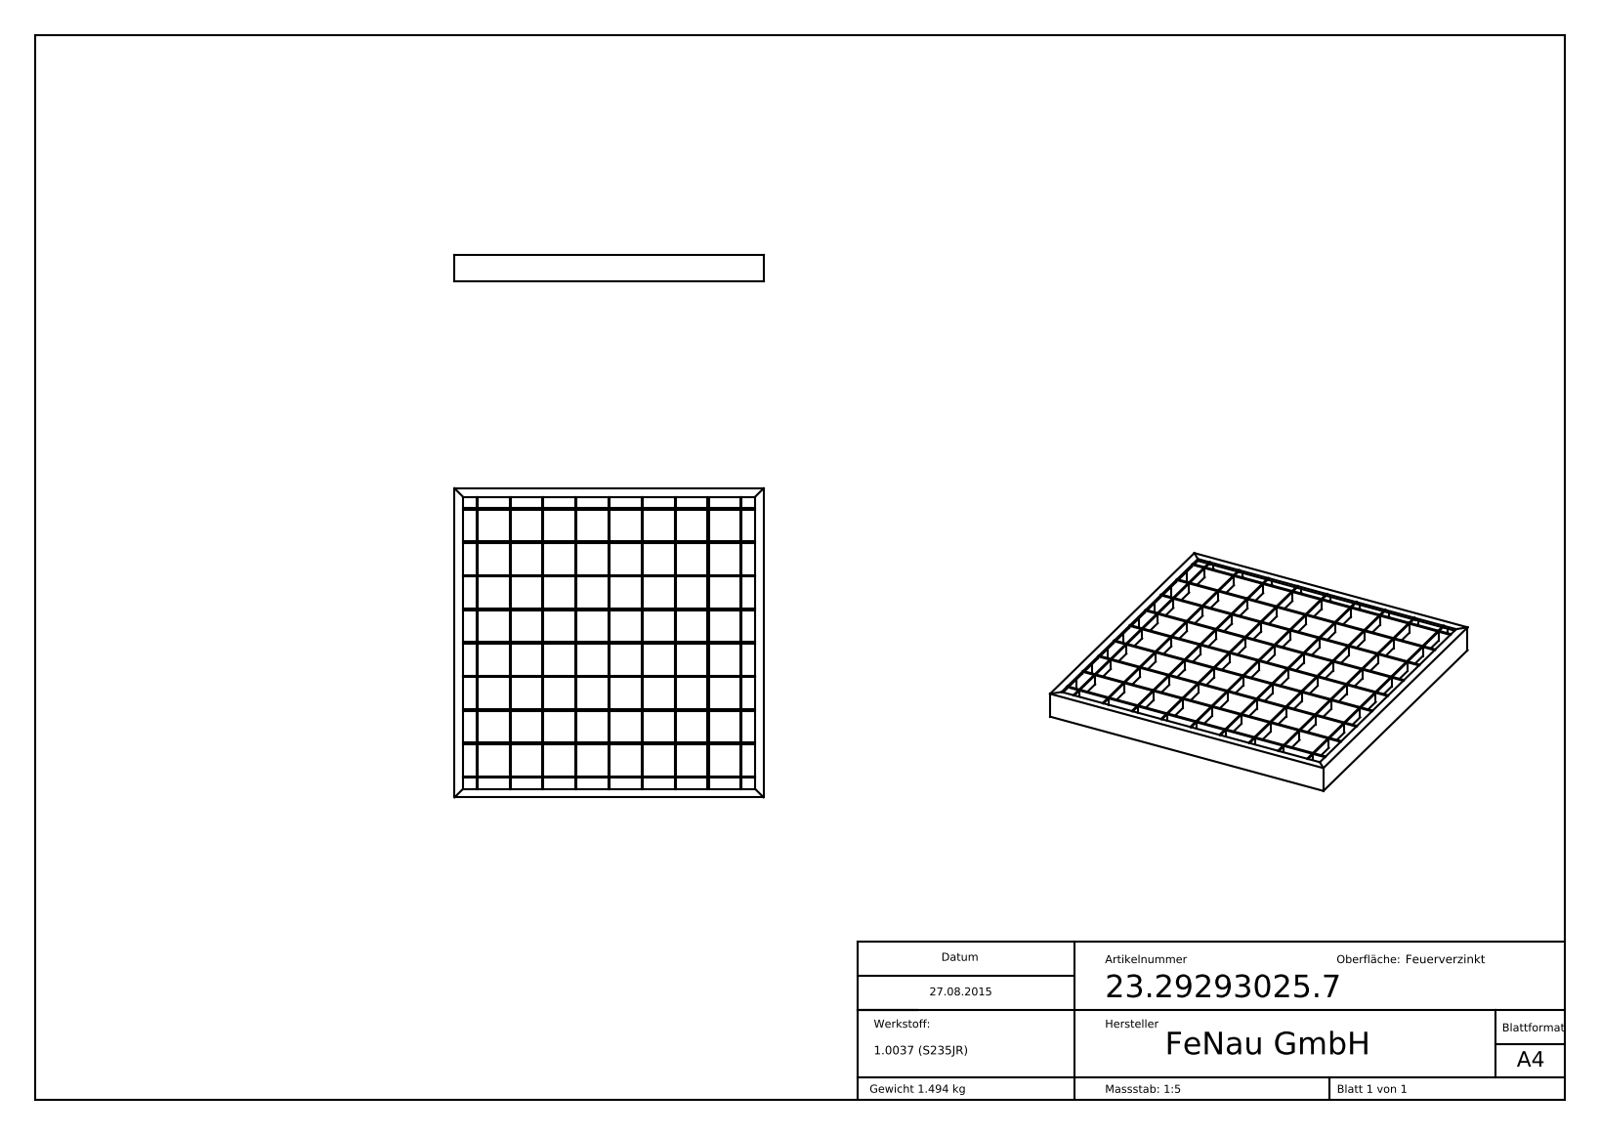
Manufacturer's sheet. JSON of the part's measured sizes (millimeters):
{"part_name": "23-29293025-7", "step_written_by": "SolidWorks 2015 (CONFIG_CONTROL_DESIGN)", "units": "millimeters", "bodies": {"solids": 1, "faces": 398, "planar": 398, "cylindrical": 0, "other": 0}, "overall_size": [290, 290, 25], "volume_mm3": 191550, "surface_area_mm2": 262050, "face_to_face_distances": [31.5, 63, 94.5, 30, 126, 93, 1.5, 157.5, 33, 61.5]}
